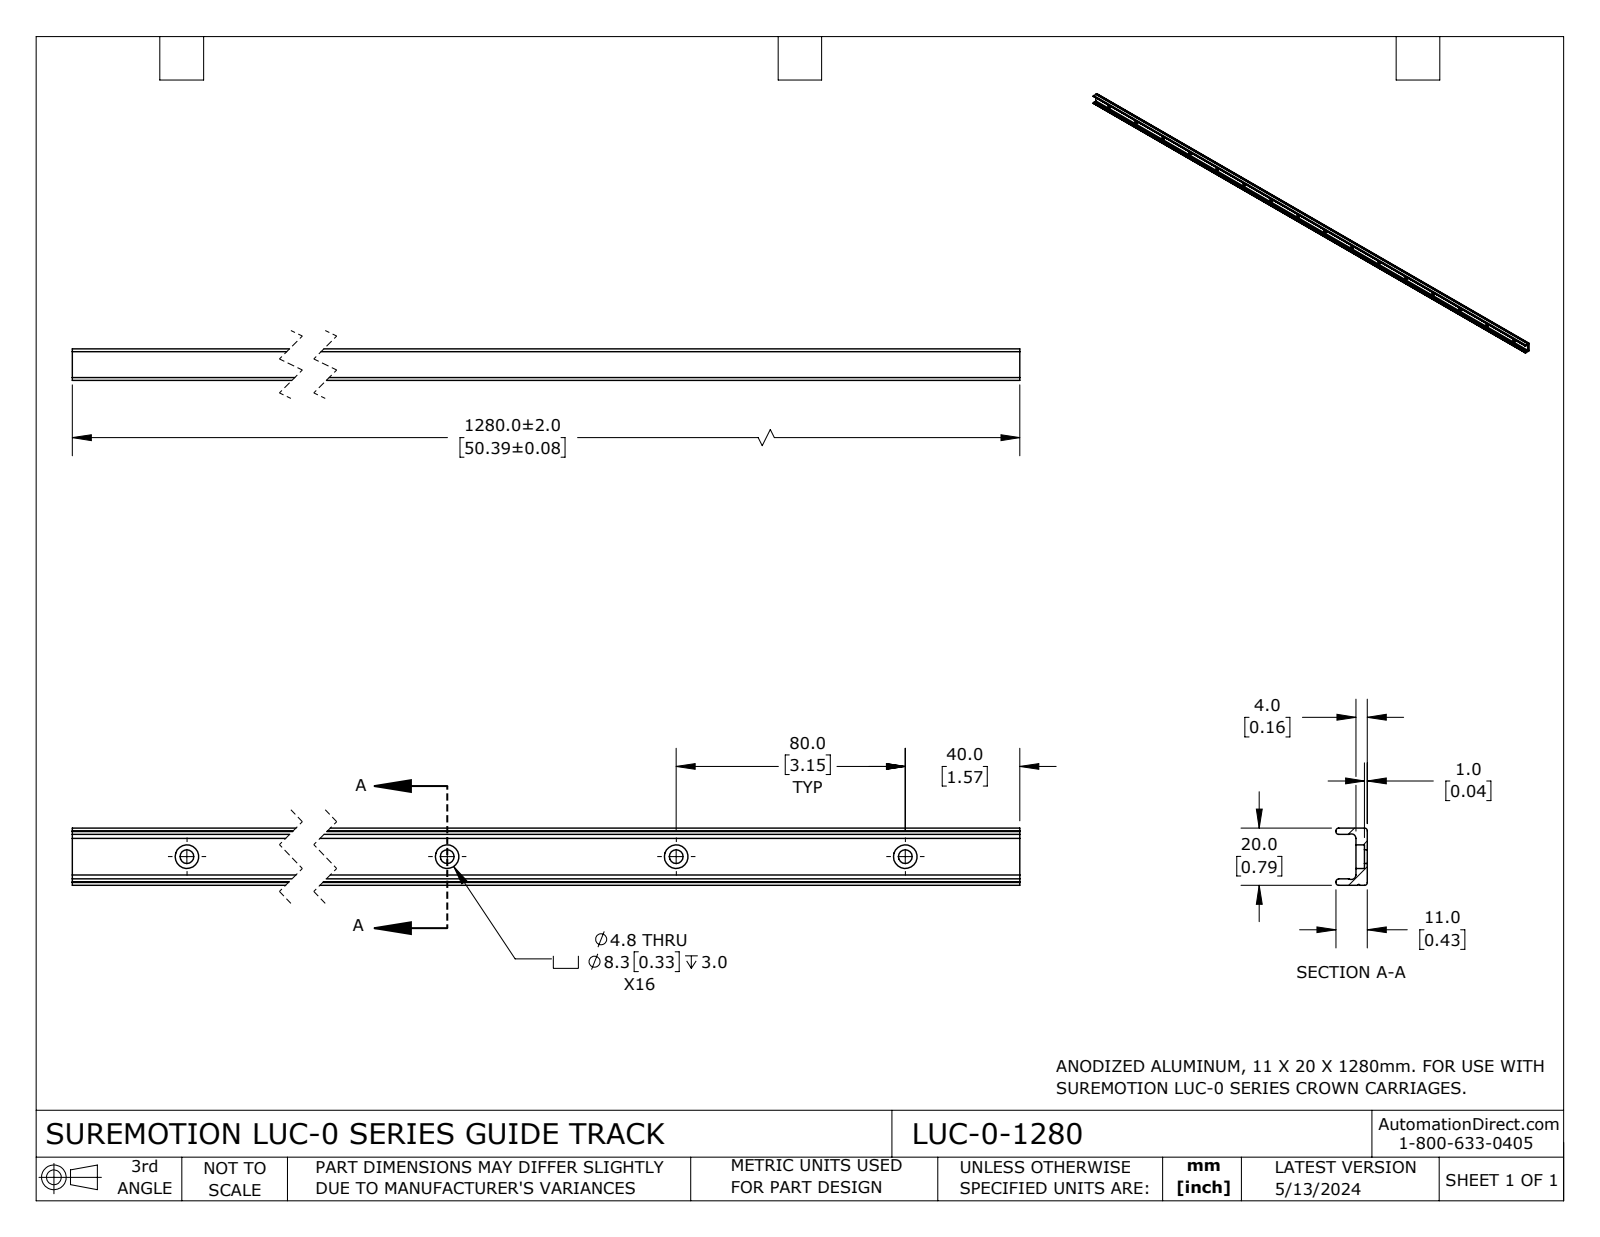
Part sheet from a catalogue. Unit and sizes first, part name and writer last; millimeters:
Units: millimetres
Overall size (bounding box): 1280 × 20 × 11
Round holes (diameter × count): ⌀4.8 ×16, ⌀8.3 ×9, ⌀8.3 ×7
Partial cylindrical surfaces — rounded edges, fillets, slot ends (radius × count): R1 ×8, R1.6 ×2, R0.3 ×1
Main face-to-face distances: 4, 20, 2.2, 17.8, 15.5, 11, 7, 1, 3, 10
Hole centre spacings: 80, 160, 240, 320, 400, 480, 560, 640
Volume: 138 100 mm³ · Surface area: 94 390 mm²
Bodies: 1 solid, 102 faces (27 planar, 75 cylindrical, 0 other)
Part name (STEP PRODUCT): LUC-0-1280
STEP written by: SolidWorks 2023 (CONFIG_CONTROL_DESIGN)
